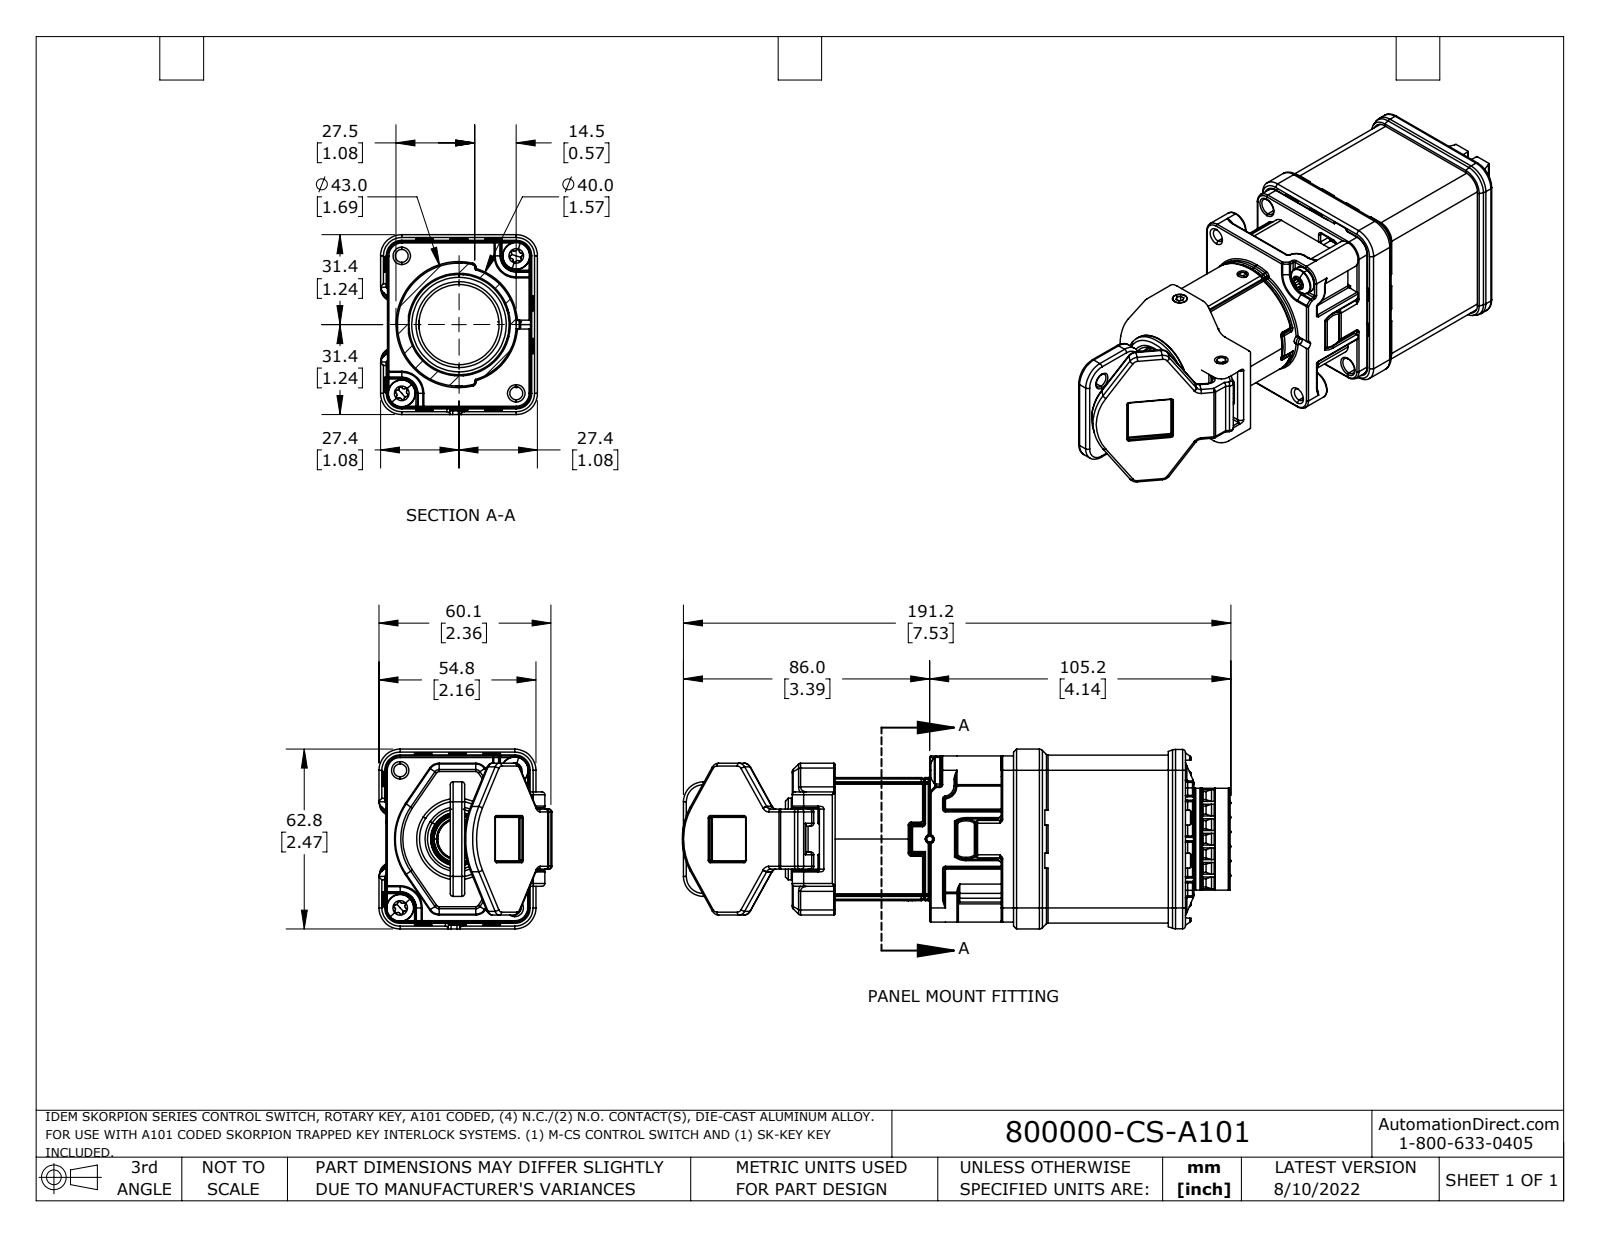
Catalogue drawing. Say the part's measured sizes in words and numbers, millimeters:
The part is named "800000-CS-A101". Its 3-D file was written by "SolidWorks 2021 (AUTOMOTIVE_DESIGN)". It is 4 solids with 2963 faces: 1116 planar, 956 cylindrical and 891 other. Overall it measures 191.6 by 62.8 by 60.4 millimeters. Its volume is 261 000 cubic millimeters and its surface area 105 000 square millimeters. Round holes: 16 of diameter 4, 4 of diameter 3, 4 of diameter 4.5, 3 of diameter 2.5, 3 of diameter 3.4, 3 of diameter 6, 2 of diameter 5.5, 2 of diameter 5.8, 1 of diameter 2, 1 of diameter 3, 1 of diameter 3.1, 1 of diameter 3.5. Round bosses or shafts: 16 of diameter 3.8, 4 of diameter 3, 3 of diameter 5, 2 of diameter 9.5, 2 of diameter 6.1, 1 of diameter 40, 1 of diameter 36, 1 of diameter 35. Partial cylindrical surfaces (rounded edges, fillets, slot ends): 276 of radius 0.5, 109 of radius 1, 34 of radius 0.3, 24 of radius 0.6, 17 of radius 1.5, 15 of radius 3, 12 of radius 4, 8 of radius 0.8. The main face-to-face distances are 2, 56.6, 7.1, 5, 48, 8.3, 9.1, 49.5, 47.5, 22.5. The hole center spacings are 5.1, 11.9, 10.2, 14.8, 15.2, 18.7, 10.8, 20.3.
